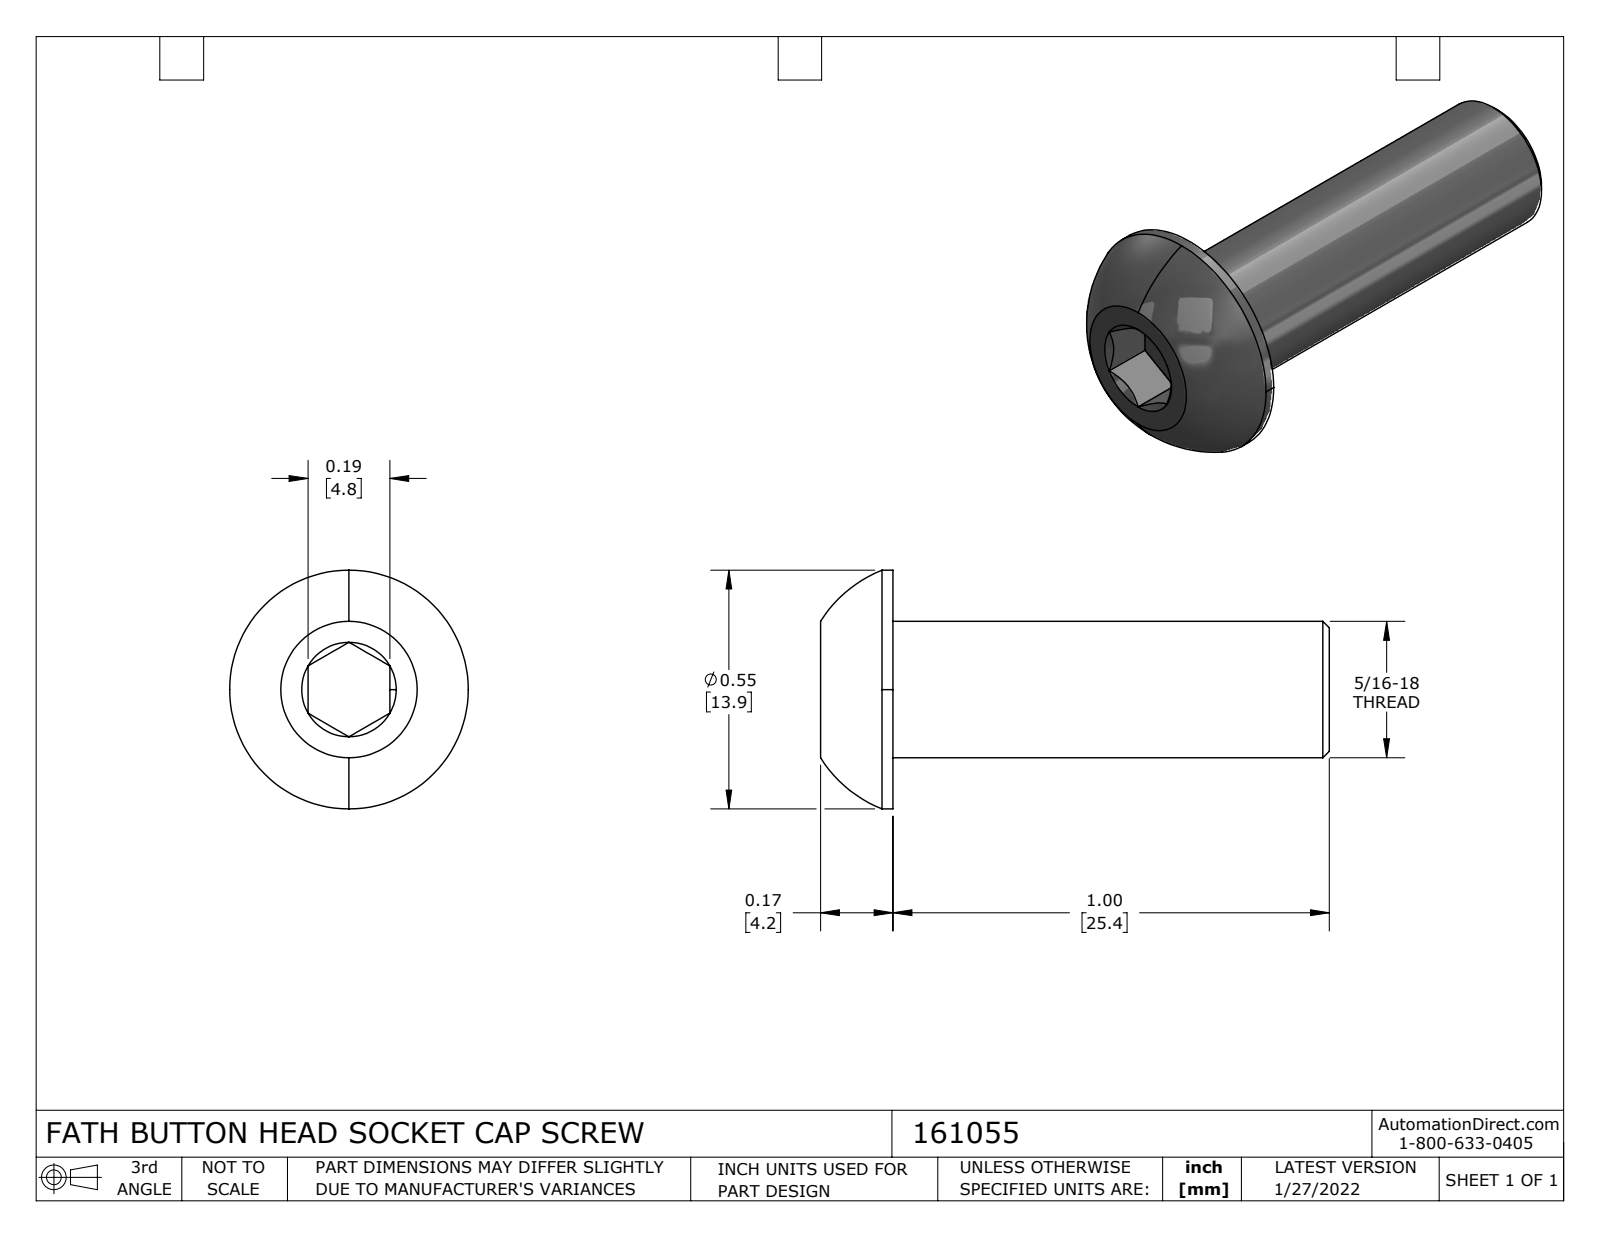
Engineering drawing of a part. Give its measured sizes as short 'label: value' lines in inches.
name: 161055
written by: SolidWorks 2021 (CONFIG_CONTROL_DESIGN)
unit: in
bodies: 1 solid, 29 faces (12 planar, 4 cylindrical, 13 other)
size: 1.166 × 0.547 × 0.547
volume: 0.102 in³; area: 1.662 in²
bosses: 1× ⌀0.547, 1× ⌀0.313
face distances: 1, 1.166, 0.166, 0.187, 1.05, 0.05, 0.116, 0.094
